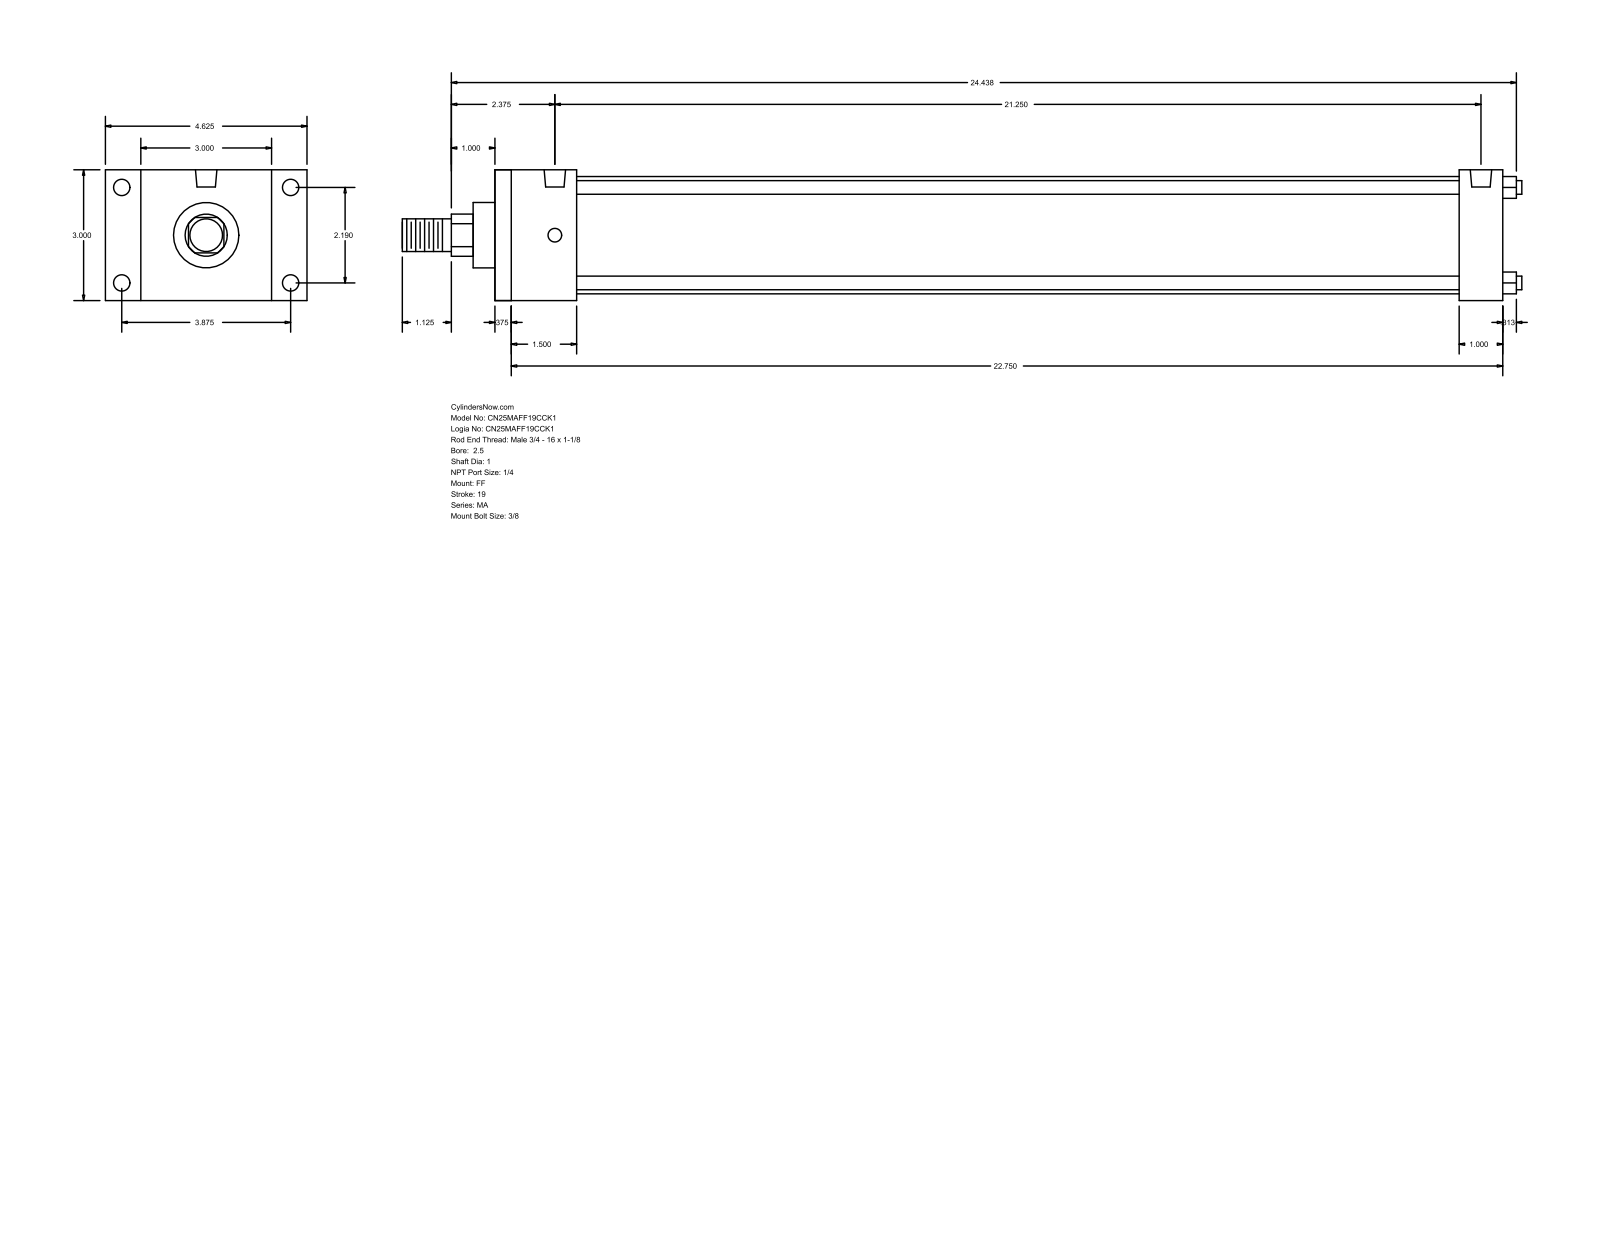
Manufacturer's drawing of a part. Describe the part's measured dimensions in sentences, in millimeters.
The part is named "MA_FF__0250_1". Its 3-D file was written by "GSSL Pune (CONFIG_CONTROL_DESIGN)". It is 0 solids with 92 faces: 64 planar, 28 cylindrical and 0 other. Overall it measures 652.46 by 117.47 by 76.2 millimeters. Round holes: 4 of diameter 7.94, 4 of diameter 9.53, 2 of diameter 12.49. Round bosses or shafts: 4 of diameter 7.94, 1 of diameter 68.33, 1 of diameter 38.1, 1 of diameter 25.4, 1 of diameter 19.05. Partial cylindrical surfaces (rounded edges, fillets, slot ends): 1 of radius 12.29. The main face-to-face distances are 76.2, 587.37, 577.85, 9.52, 25.39, 47.63, 561.98, 38.11, 552.46, 514.35. The hole center spacings are 55.62, 98.42, 113.05, 539.75.
